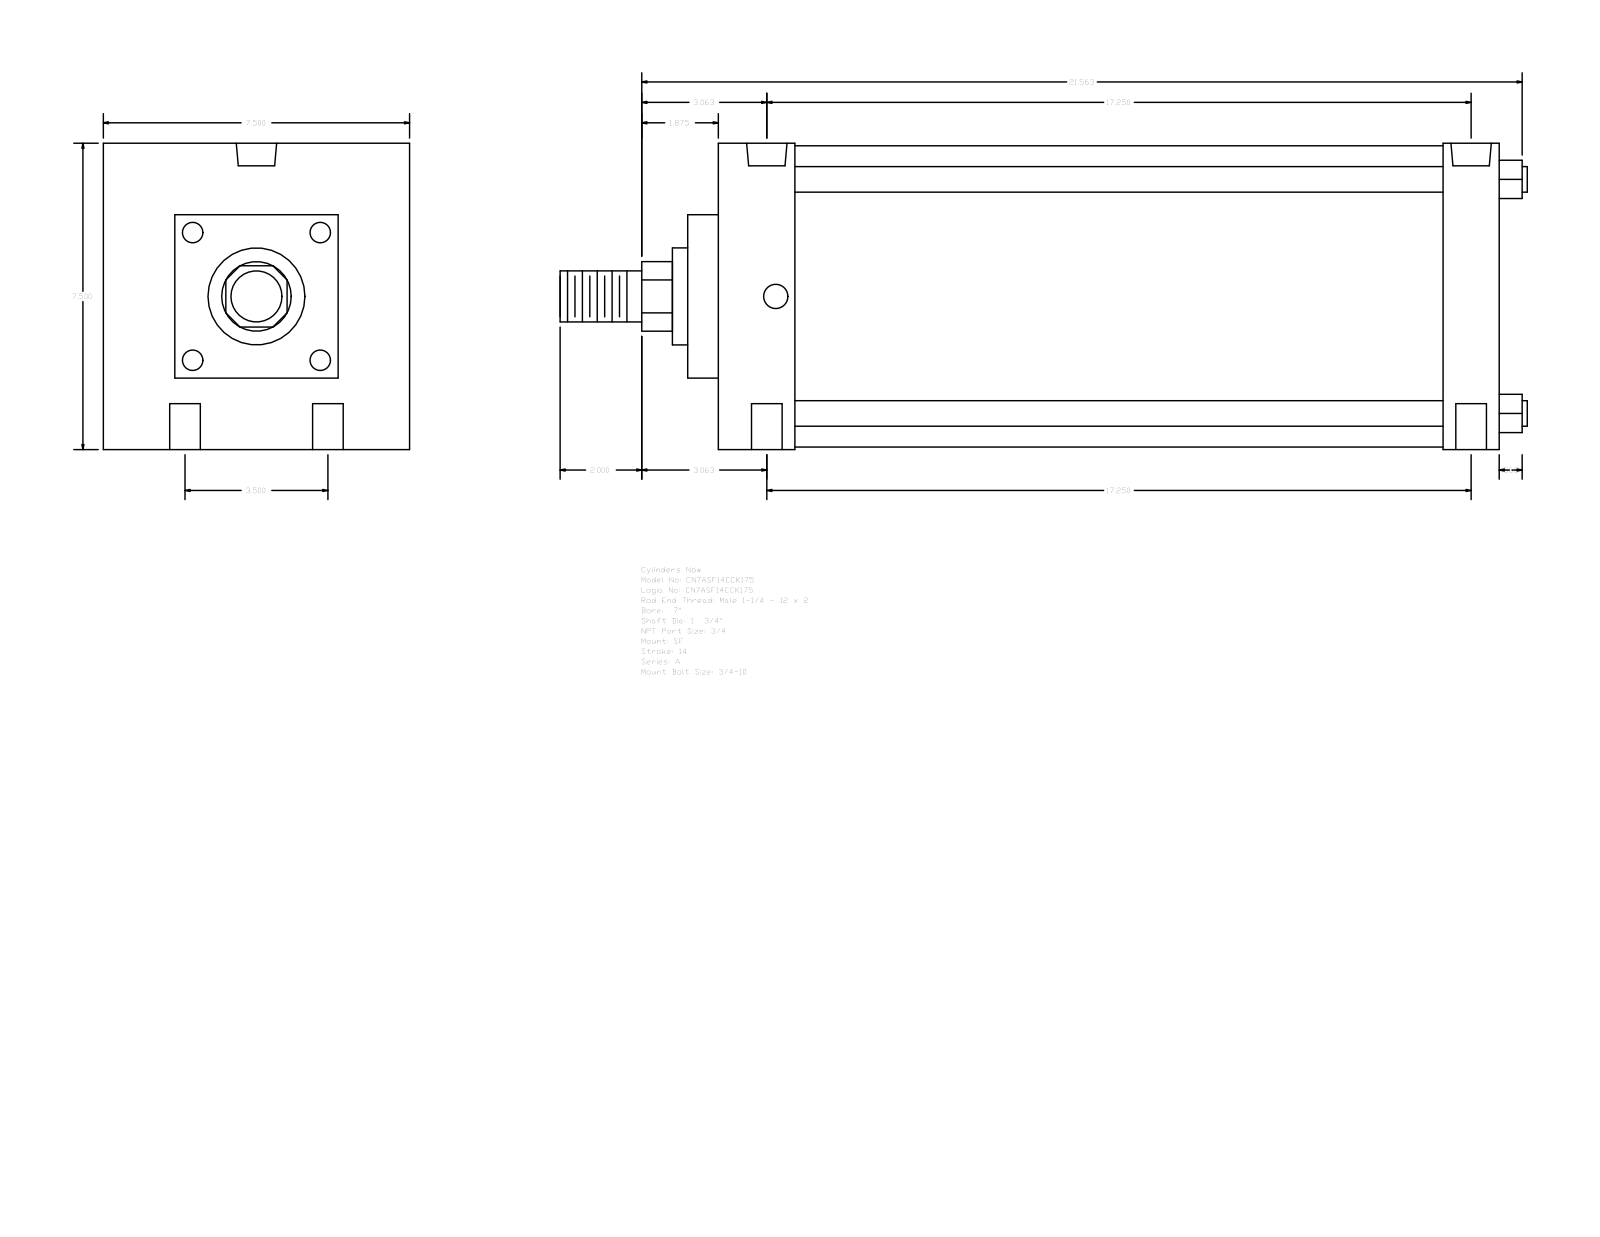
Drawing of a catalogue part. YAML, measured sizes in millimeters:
part_name: "A_SF__0700_1.75"
step_written_by: "GSSL Pune (CONFIG_CONTROL_DESIGN)"
units: millimeters
bodies: {solids: 0, faces: 93, planar: 67, cylindrical: 26, other: 0}
overall_size: [601.66, 190.5, 190.5]
round_holes:
  - {diameter: 19.05, count: 4}
  - {diameter: 15.08, count: 2}
  - {diameter: 25.12, count: 2}
round_bosses_or_shafts:
  - {diameter: 15.88, count: 4}
  - {diameter: 187.32, count: 1}
  - {diameter: 60.33, count: 1}
  - {diameter: 44.45, count: 1}
  - {diameter: 31.75, count: 1}
partial_cylinders:
  - {radius: 21.63, count: 1}
face_to_face_distances: [190.5, 485.78, 146.05, 19.05, 47.63, 450.86, 403.23, 438.15, 34.92, 44.45]
hole_center_spacings: [44.45, 440.4, 438.15, 88.9, 447.08, 427.03]
